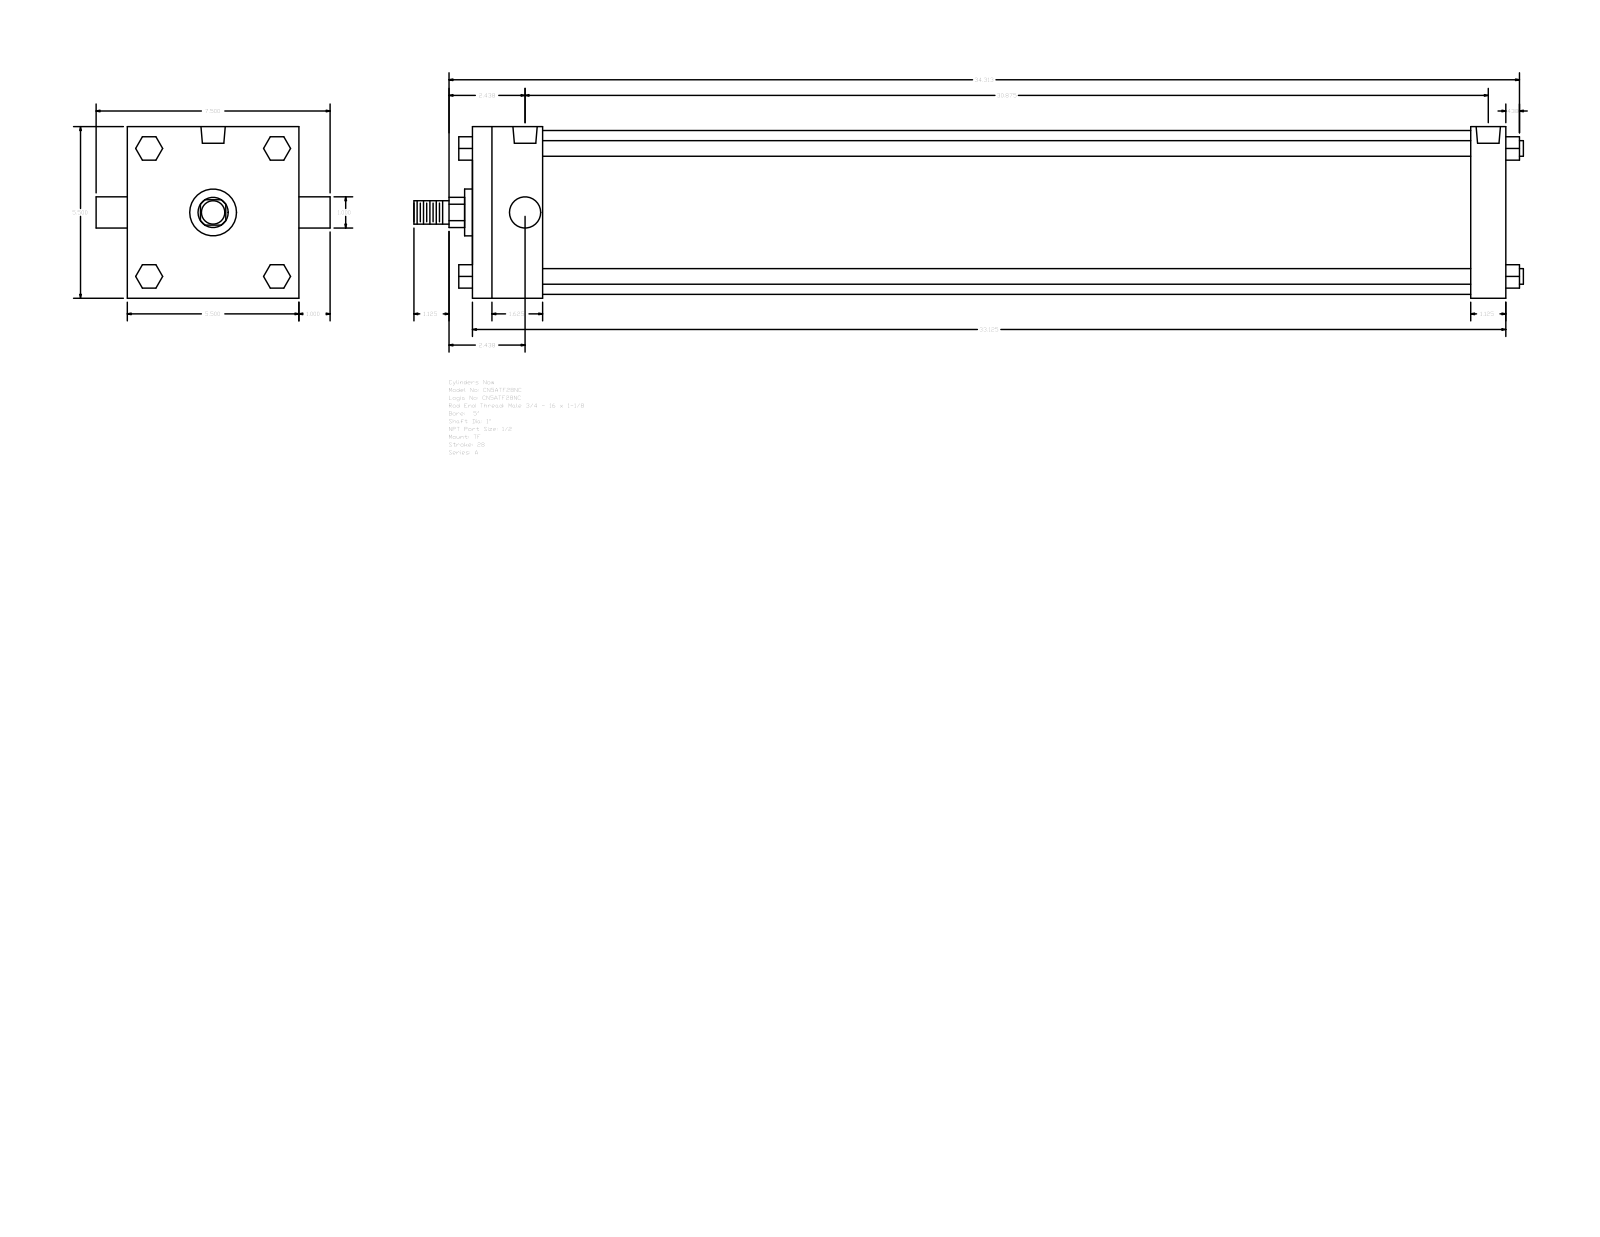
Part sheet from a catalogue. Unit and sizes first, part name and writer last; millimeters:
Units: millimetres
Overall size (bounding box): 903.29 × 190.5 × 139.7
Round holes (diameter × count): ⌀8.73 ×3, ⌀19.77 ×2
Round bosses / shafts (diameter × count): ⌀12.7 ×4, ⌀25.4 ×2, ⌀133.35 ×1, ⌀38.1 ×1, ⌀19.05 ×1
Partial cylindrical surfaces — rounded edges, fillets, slot ends (radius × count): R12.29 ×1
Main face-to-face distances: 139.7, 841.37, 28.57, 812.8, 57.15, 755.65, 784.22, 19.05, 52.07, 90.18
Hole centre spacings: 2.39, 781.84, 779.45, 784.23
Bodies: 0 solids, 120 faces (92 planar, 28 cylindrical, 0 other)
Part name (STEP PRODUCT): A_TF__0500_1
STEP written by: GSSL Pune (CONFIG_CONTROL_DESIGN)
